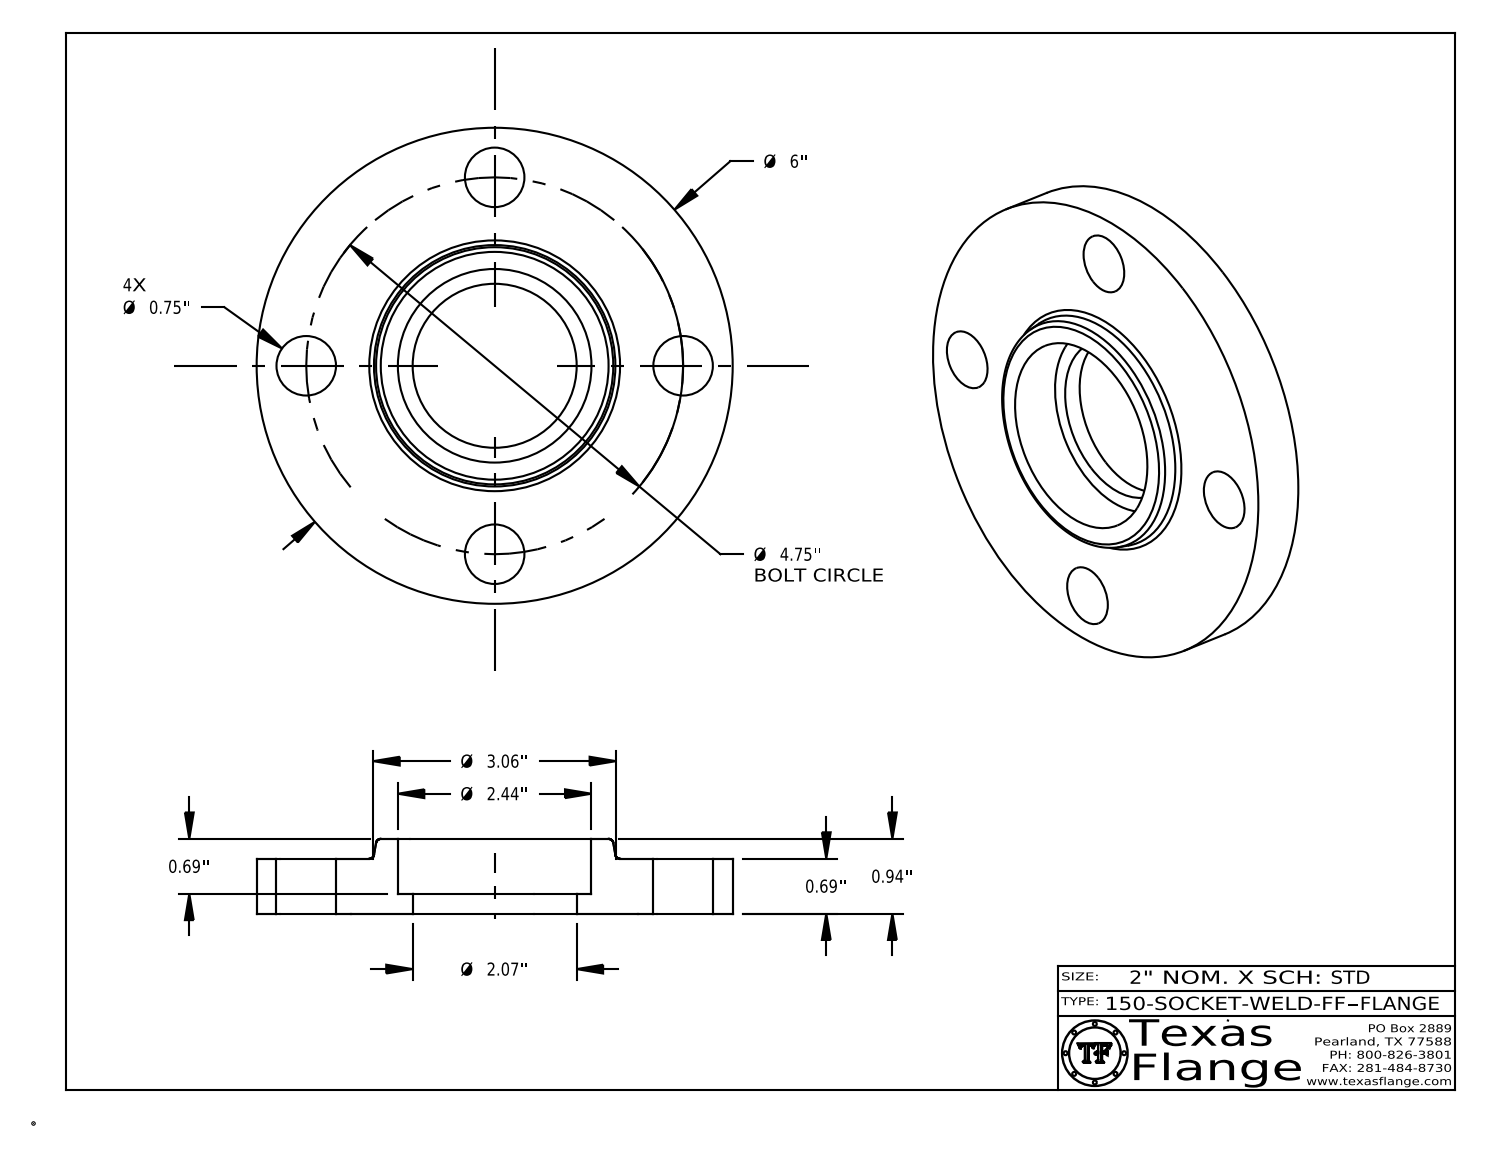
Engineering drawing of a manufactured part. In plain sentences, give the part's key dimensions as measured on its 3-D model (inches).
The part is named "150-SOCKET-WELD-FF". Its 3-D file was written by "CATIA V5 STEP AP214 (AUTOMOTIVE_DESIGN)". It is 1 solid with 410 faces: 370 planar, 34 cylindrical and 6 other. Overall it measures 6 by 6 by 0.94 inches. Its volume is 16.01 cubic inches and its surface area 74.49 square inches. Round holes: 4 of diameter 0.75, 1 of diameter 0.495, 1 of diameter 2.067, 1 of diameter 2.44. Round bosses or shafts: 8 of diameter 0.03, 1 of diameter 6, 1 of diameter 0.39. The main face-to-face distances are 0.69, 0.25, 0.94, 0.44, 0.675, 0.425, 0.015, 0.265, 0.147, 0.144. The hole center spacings are 2.375, 3.359, 1.818, 4.389, 4.75.
